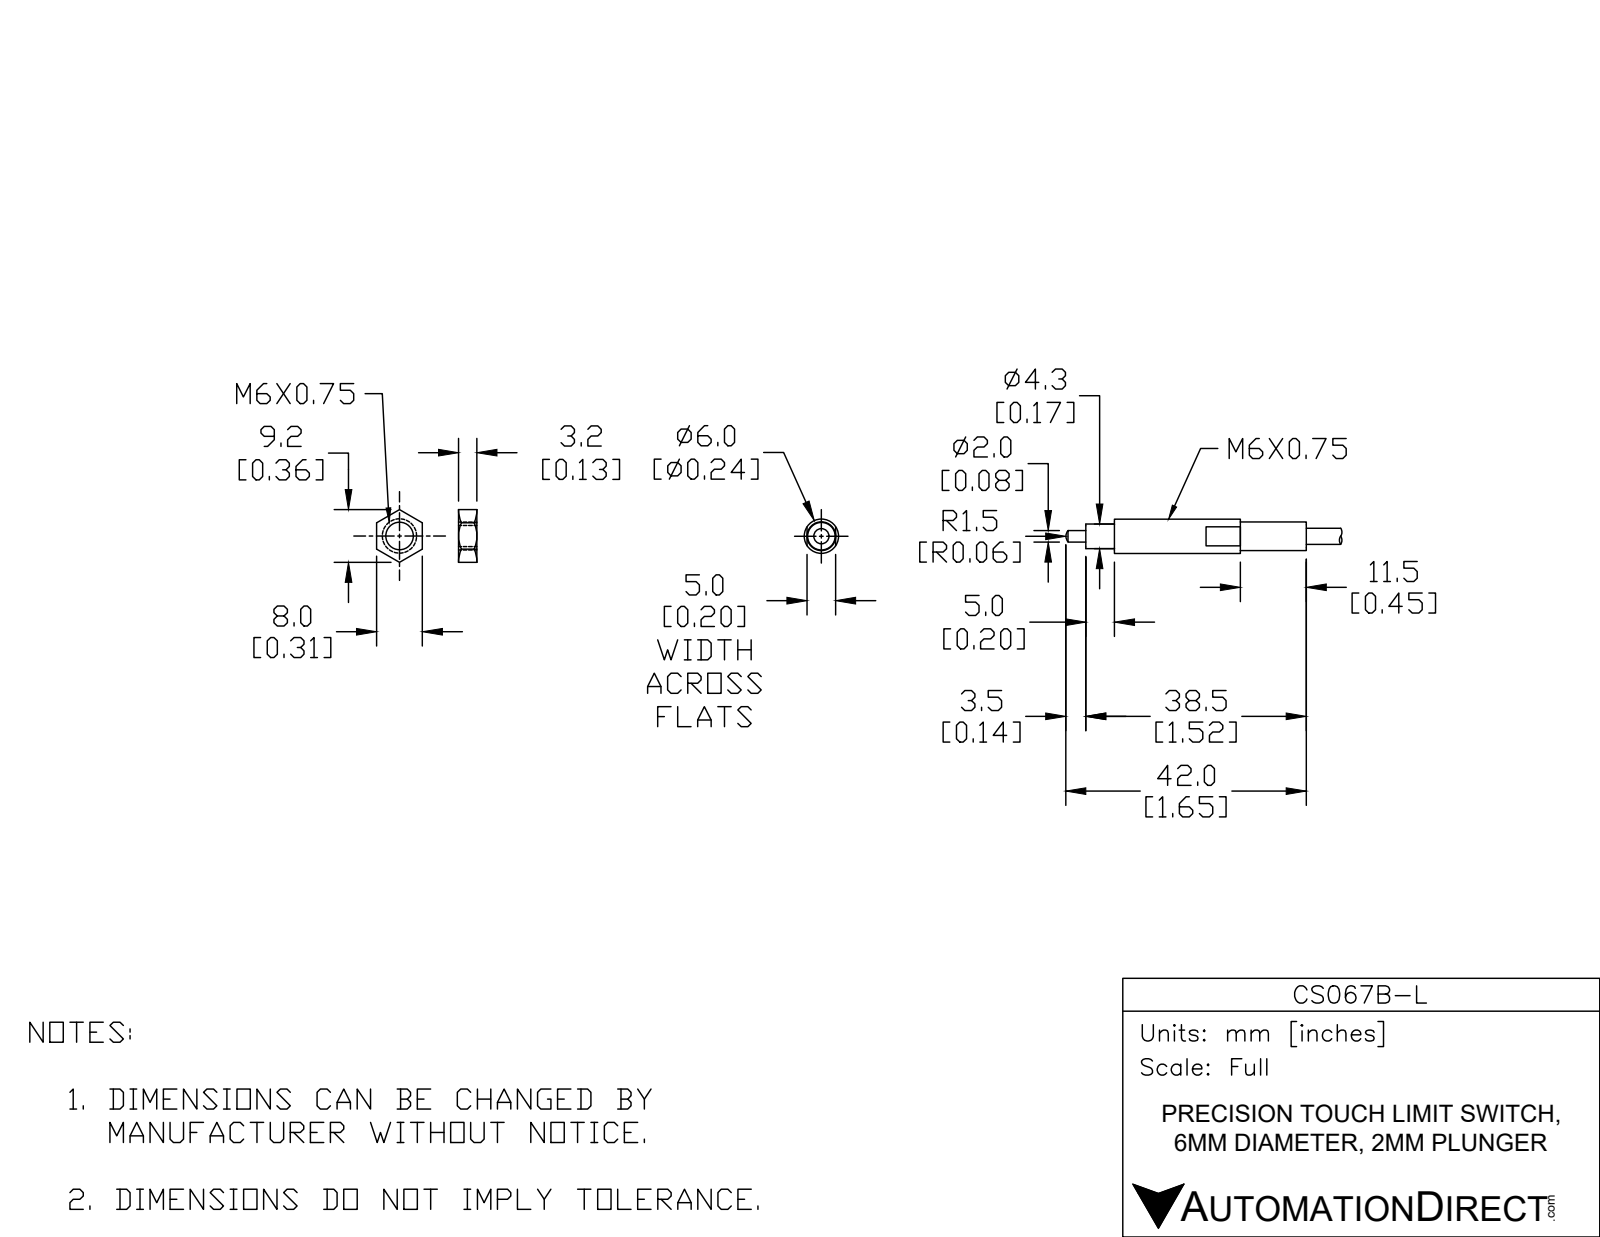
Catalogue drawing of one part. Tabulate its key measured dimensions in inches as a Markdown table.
| quantity | value |
| --- | --- |
| part name | CS067B-L |
| STEP written by | SolidWorks 2017 (AUTOMOTIVE_DESIGN) |
| units | inches |
| bodies | 1 solid, 184 faces (10 planar, 99 cylindrical, 75 other) |
| overall size | 1.89 × 0.236 × 0.236 |
| volume | 0.054 in³ |
| surface area | 1.623 in² |
| round bosses / shafts (diameter × count) | 0.236 × 1, 0.197 × 1, 0.169 × 1, 0.11 × 1, 0.079 × 1 |
| partial cylindrical surfaces (radius × count) | 0.218 × 1, 0.24 × 1 |
| main face-to-face distances | 0.197, 1.516, 1.319, 0.236, 1.752, 1.555, 0.689, 1.063, 0.866, 0.453 |
